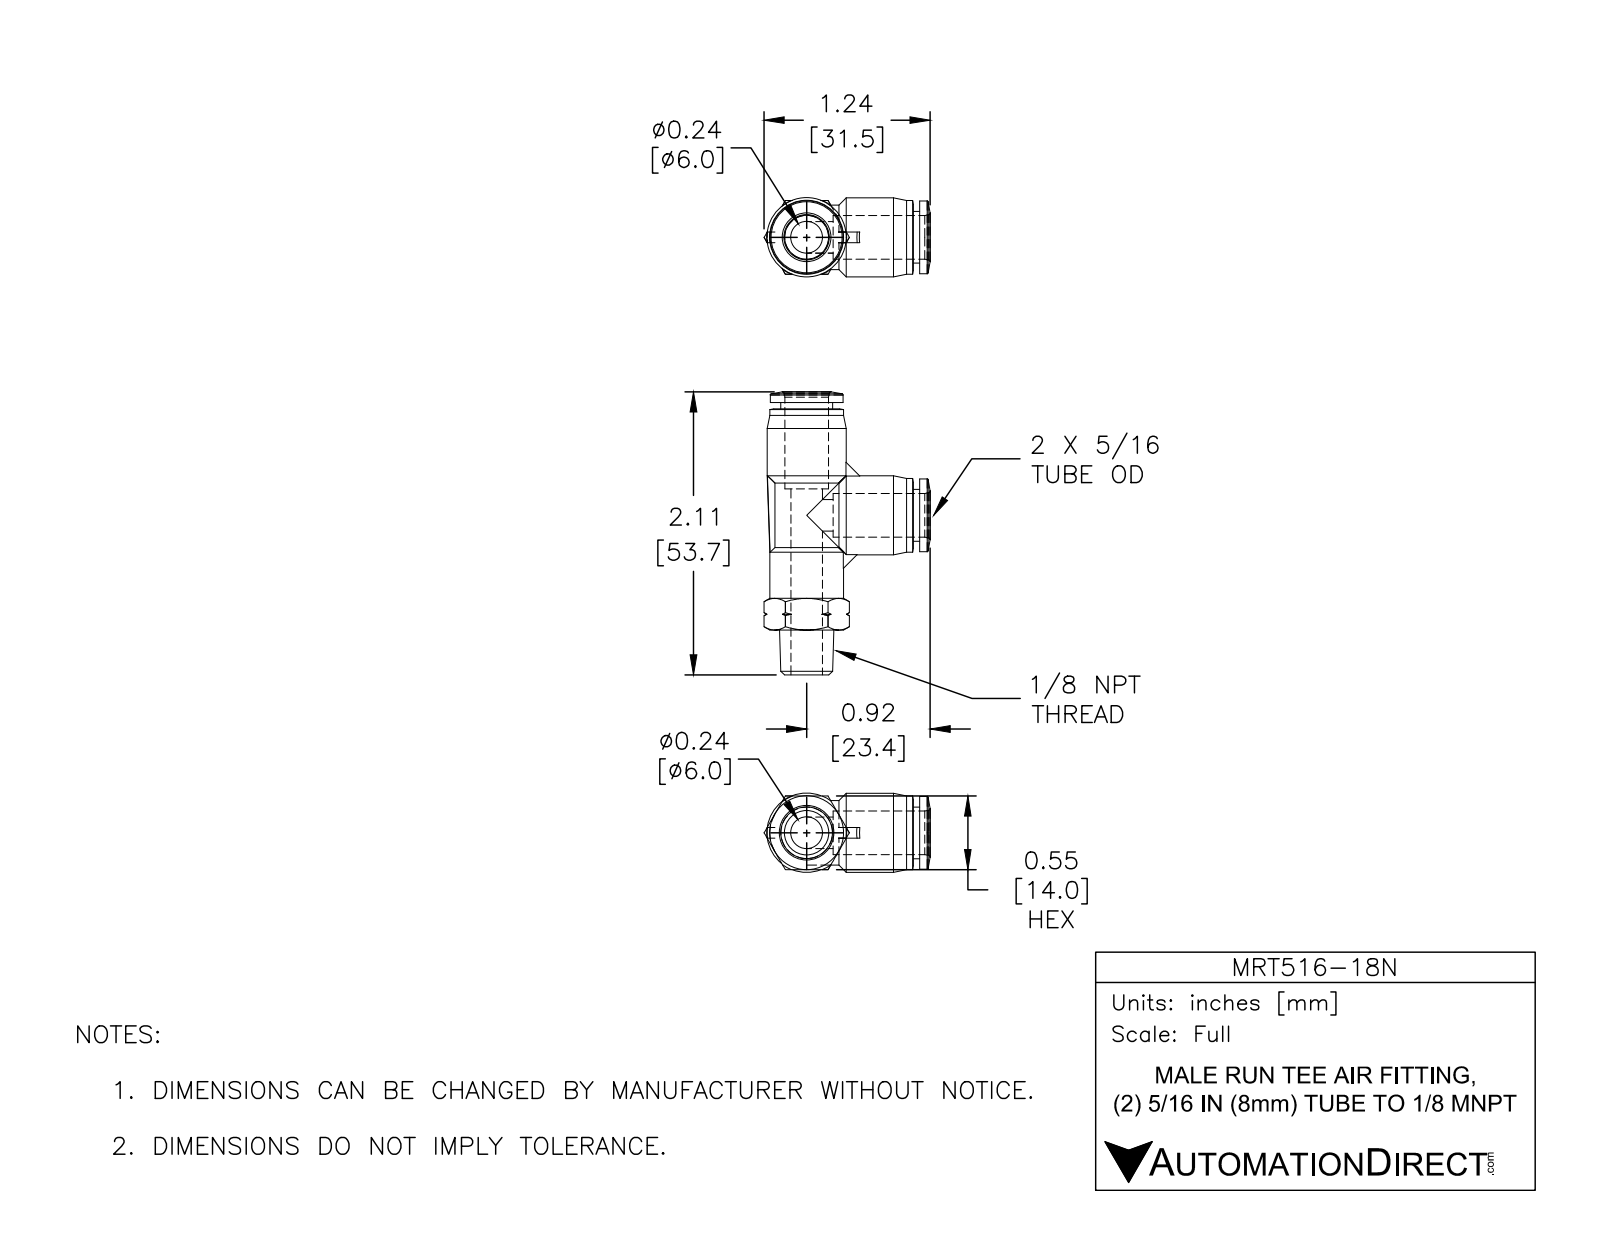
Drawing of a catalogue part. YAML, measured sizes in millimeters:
part_name: "MRT516-18N"
step_written_by: "SolidWorks 2015 (CONFIG_CONTROL_DESIGN)"
units: millimeters
bodies: {solids: 1, faces: 116, planar: 22, cylindrical: 30, other: 64}
overall_size: [53.6, 31.5, 15]
volume: 7180
surface_area: 5283
round_holes:
  - {diameter: 6, count: 2}
  - {diameter: 8.3, count: 2}
round_bosses_or_shafts:
  - {diameter: 15, count: 2}
  - {diameter: 14, count: 2}
  - {diameter: 13.8, count: 2}
  - {diameter: 12.2, count: 2}
  - {diameter: 9.8, count: 2}
face_to_face_distances: [14, 1.2, 43.2, 15.2, 16.4, 42, 6, 8, 8.5, 50.4]
